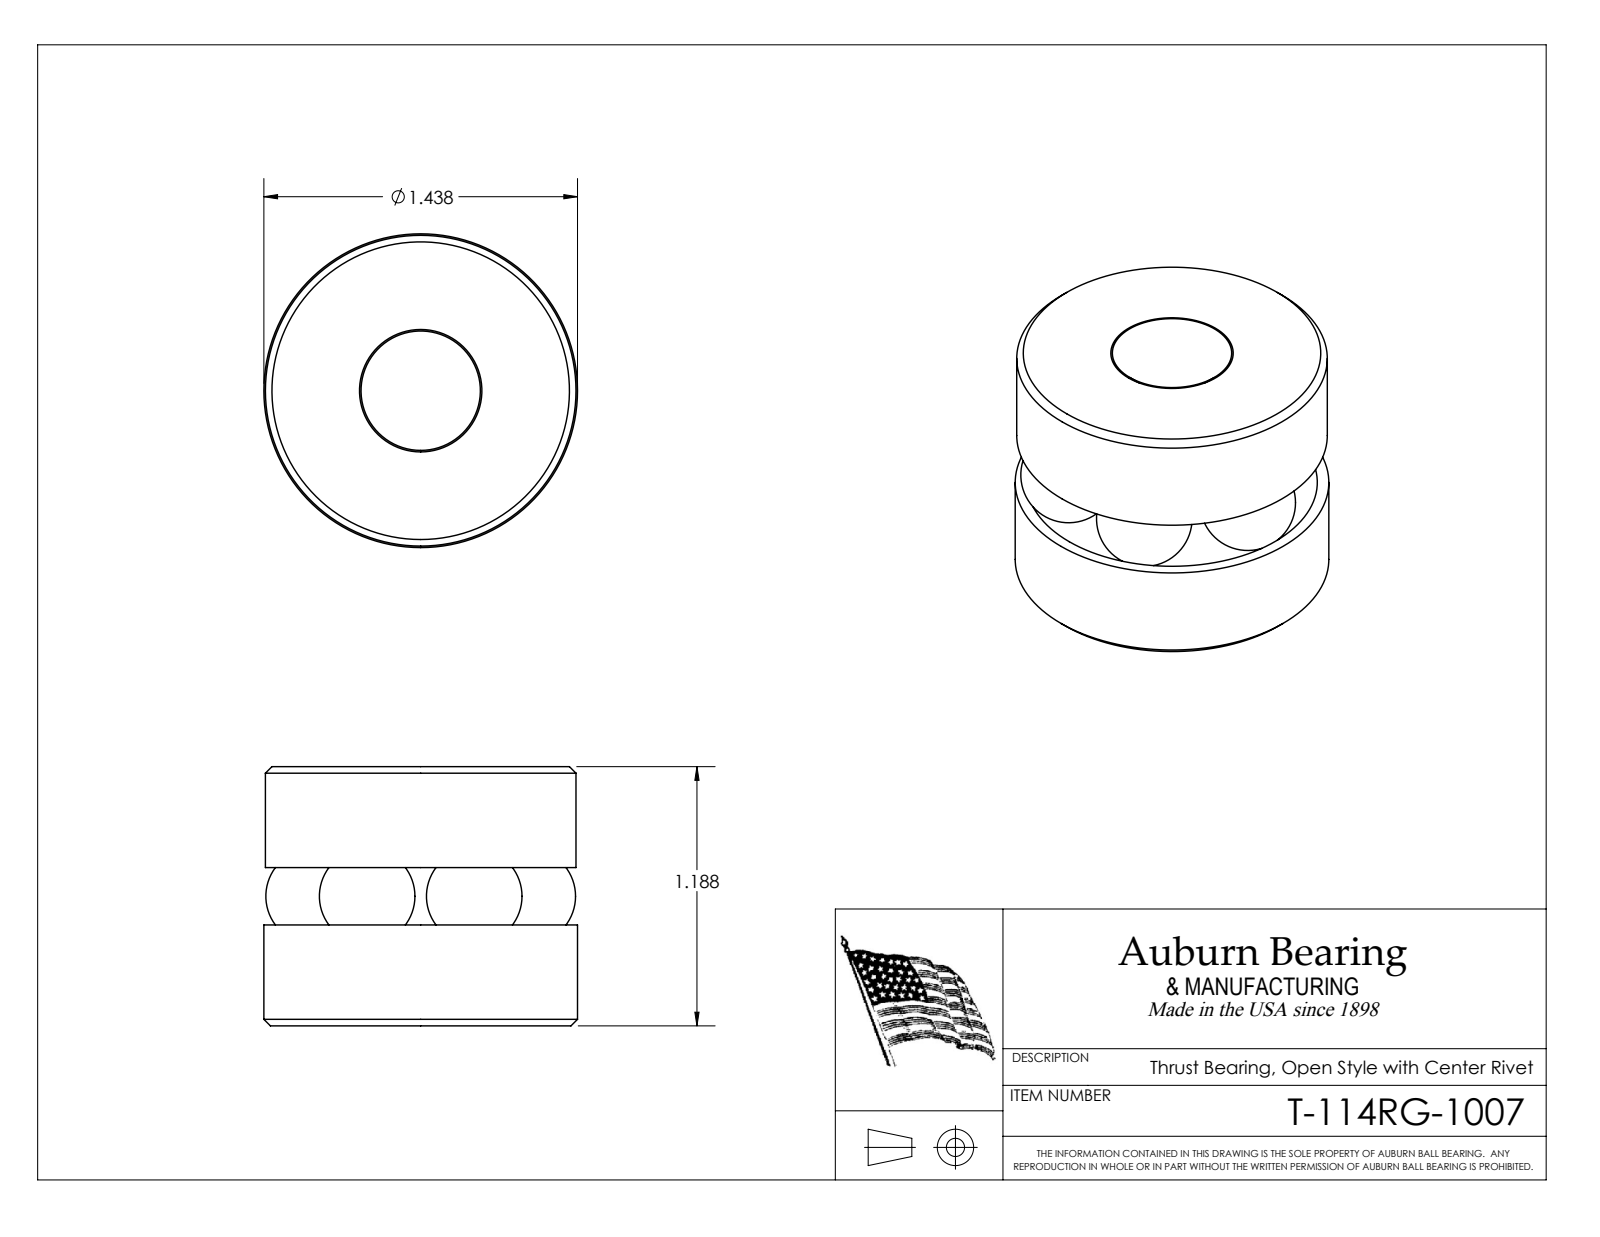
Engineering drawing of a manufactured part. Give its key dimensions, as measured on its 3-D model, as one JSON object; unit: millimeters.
{"part_name": "T-114RG_T-114RG-1007", "step_written_by": "SolidWorks 2016 (CONFIG_CONTROL_DESIGN)", "units": "millimeters", "bodies": {"solids": 9, "faces": 27, "planar": 8, "cylindrical": 5, "other": 14}, "overall_size": [36.5, 36.5, 30.2], "volume_mm3": 26580, "surface_area_mm2": 10670, "round_holes": [[6.6, 1]], "round_bosses_or_shafts": [[36.5, 1], [36.1, 1], [6.4, 1]], "face_to_face_distances": [30.1, 11.7, 18.4, 6.7]}
